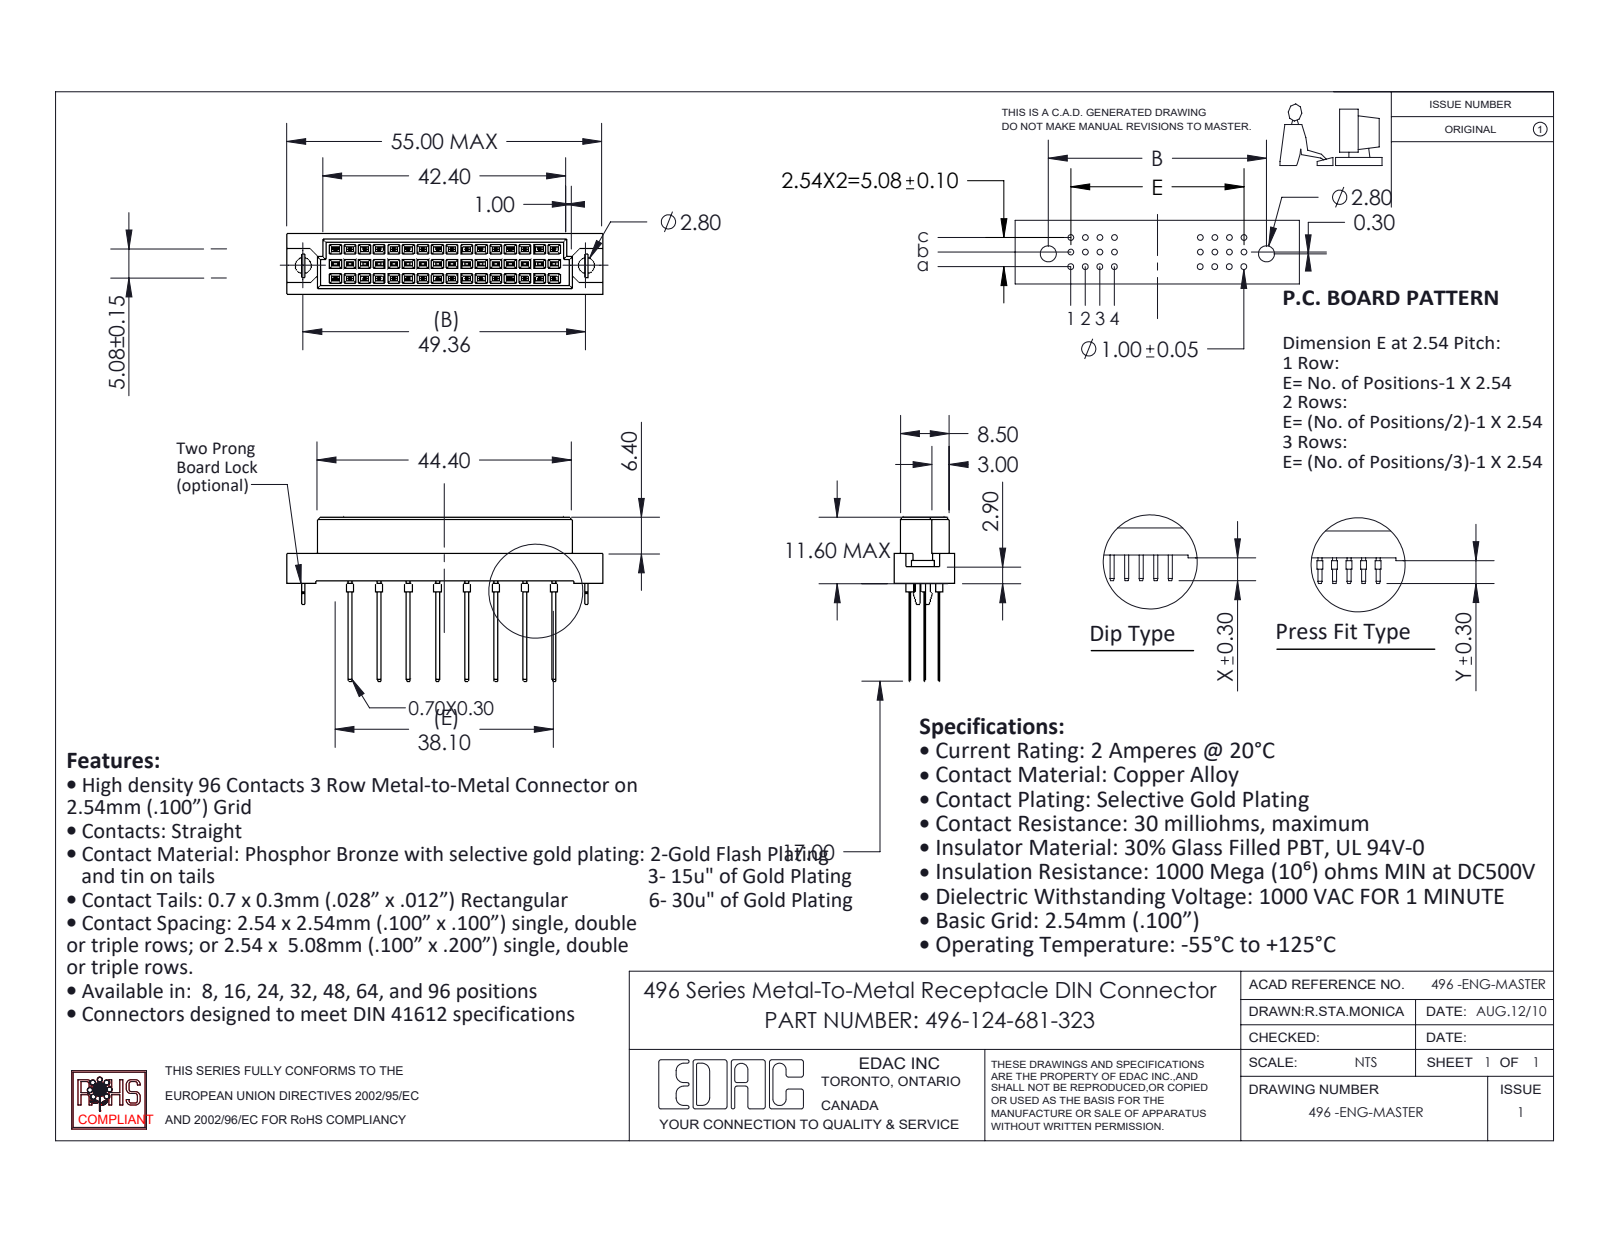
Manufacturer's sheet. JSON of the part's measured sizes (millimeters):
{"part_name": "496-290_81; 496 Part_48; 496 Bore-lock; 496-124-681-323", "step_written_by": "SolidWorks 2020 (CONFIG_CONTROL_DESIGN)", "units": "millimeters", "bodies": {"solids": 27, "faces": 1134, "planar": 1080, "cylindrical": 54, "other": 0}, "overall_size": [55, 28.6, 10.6], "volume_mm3": 4740, "surface_area_mm2": 5424, "round_holes": [[2.8, 2]], "round_bosses_or_shafts": [[1, 24]], "partial_cylinders_radius": [[0.53, 1]], "face_to_face_distances": [2.54, 5.08, 1.05, 9.55, 0.56, 0.55, 0.81, 2.84, 4.4, 1.56], "hole_center_spacings": [49.36]}
